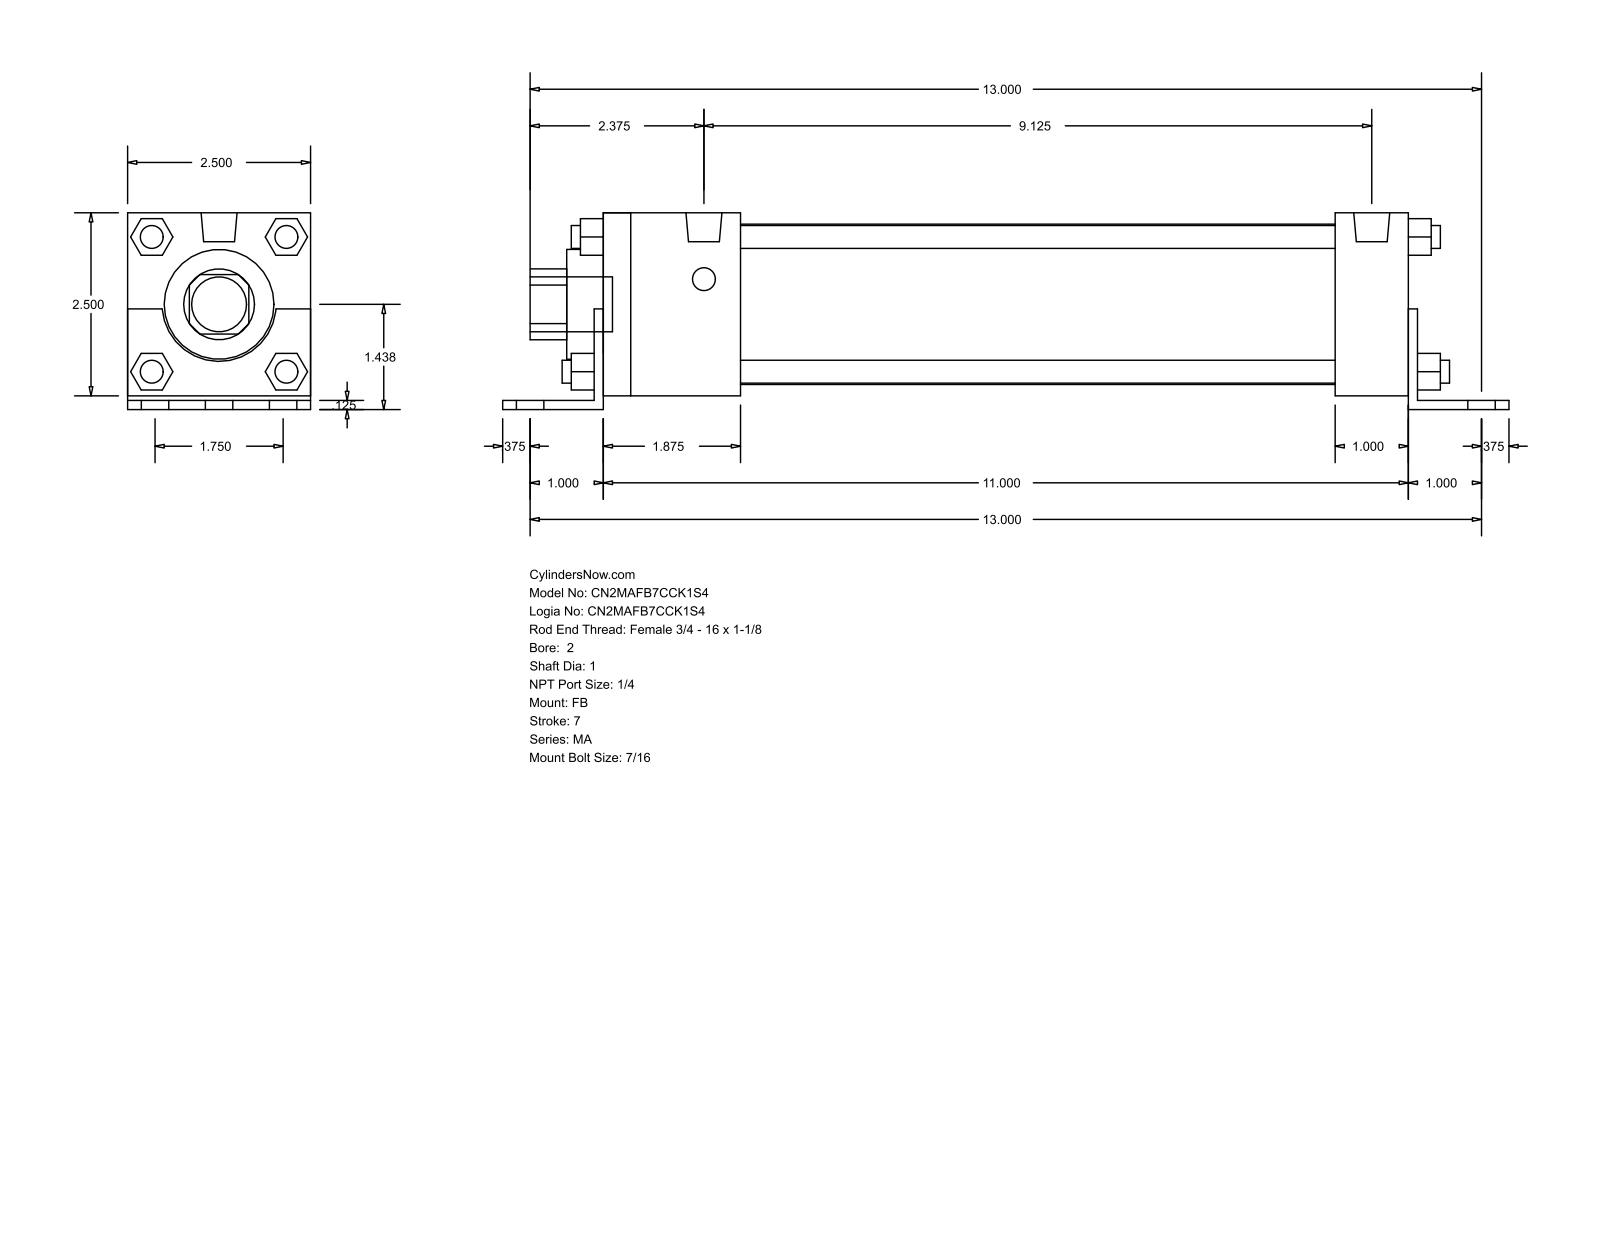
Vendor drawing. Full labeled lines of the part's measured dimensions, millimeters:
Part name (STEP PRODUCT): MA_FB__0200_1
STEP written by: GSSL Pune (CONFIG_CONTROL_DESIGN)
Units: millimetres
Bodies: 0 solids, 140 faces (105 planar, 35 cylindrical, 0 other)
Overall size (bounding box): 349.25 × 68.26 × 63.5
Round holes (diameter × count): ⌀25.4 ×1, ⌀38.1 ×1, ⌀55.63 ×1
Round bosses / shafts (diameter × count): ⌀7.94 ×8, ⌀11.11 ×6, ⌀12.49 ×2, ⌀19.05 ×1
Partial cylindrical surfaces — rounded edges, fillets, slot ends (radius × count): R12.29 ×1, R19.81 ×1
Main face-to-face distances: 63.5, 3.17, 4.76, 68.26, 1.59, 65.09, 12.7, 3.18, 279.4, 282.58
